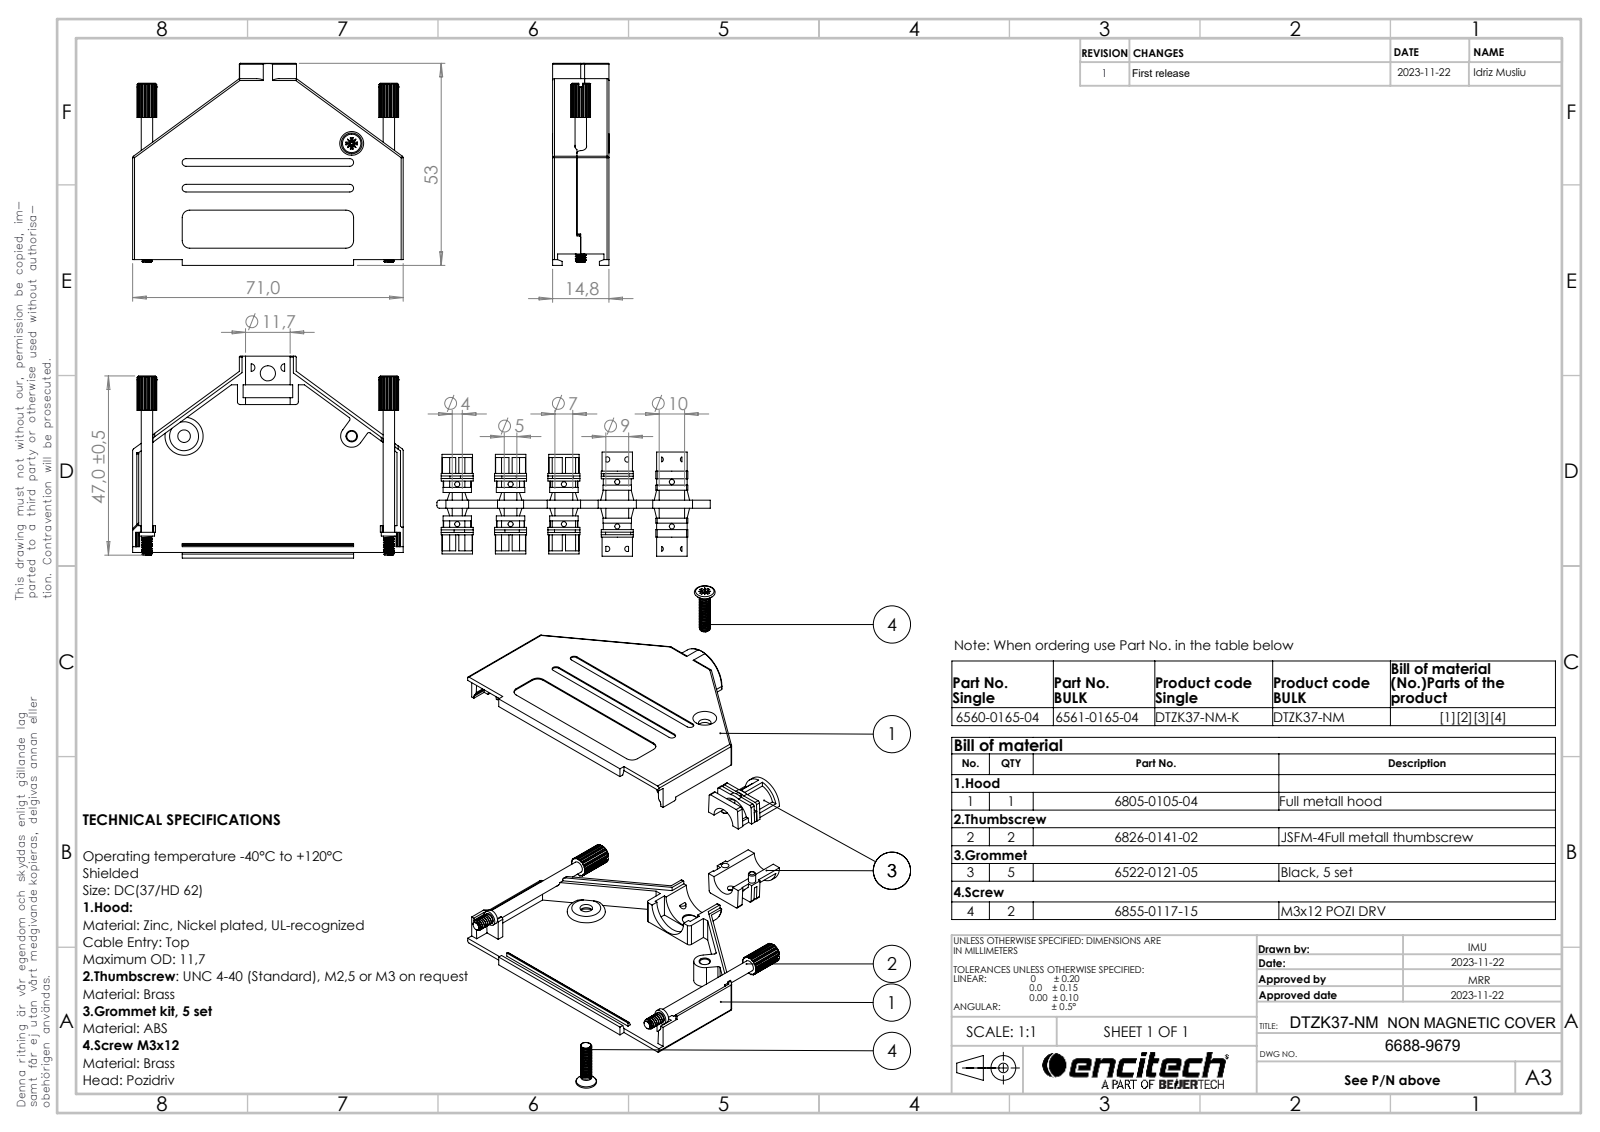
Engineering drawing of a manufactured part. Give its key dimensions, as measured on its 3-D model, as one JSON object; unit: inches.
{"part_name": "6522-0121-05 (7mm); 6855-0117-15; 6688-9679; 6805-0105-04 (+1 more)", "step_written_by": "SolidWorks 2021 (AUTOMOTIVE_DESIGN)", "units": "inches", "bodies": {"solids": 8, "faces": 802, "planar": 444, "cylindrical": 276, "other": 82}, "overall_size": [2.795, 2.087, 0.589], "volume_in3": 0.78, "surface_area_in2": 31.1, "round_holes": [[0.079, 3], [0.102, 2], [0.122, 2], [0.13, 2], [0.157, 1], [0.276, 1], [0.461, 1]], "round_bosses_or_shafts": [[0.118, 4], [0.157, 2], [0.11, 2], [0.075, 2], [0.591, 1], [0.457, 1], [0.362, 1]], "partial_cylinders_radius": [[0.02, 32], [0.039, 12], [0.004, 8], [0.01, 8], [0.079, 4], [0.233, 4], [0.008, 2], [0.012, 2]], "face_to_face_distances": [0.051, 0.531, 0.48, 0.583, 0.039, 0.571, 0.52, 0.24, 0.063, 0.28], "hole_center_spacings": [0.225, 0.274, 0.811, 0.934, 1.083, 1.158, 1.25, 0.299]}
